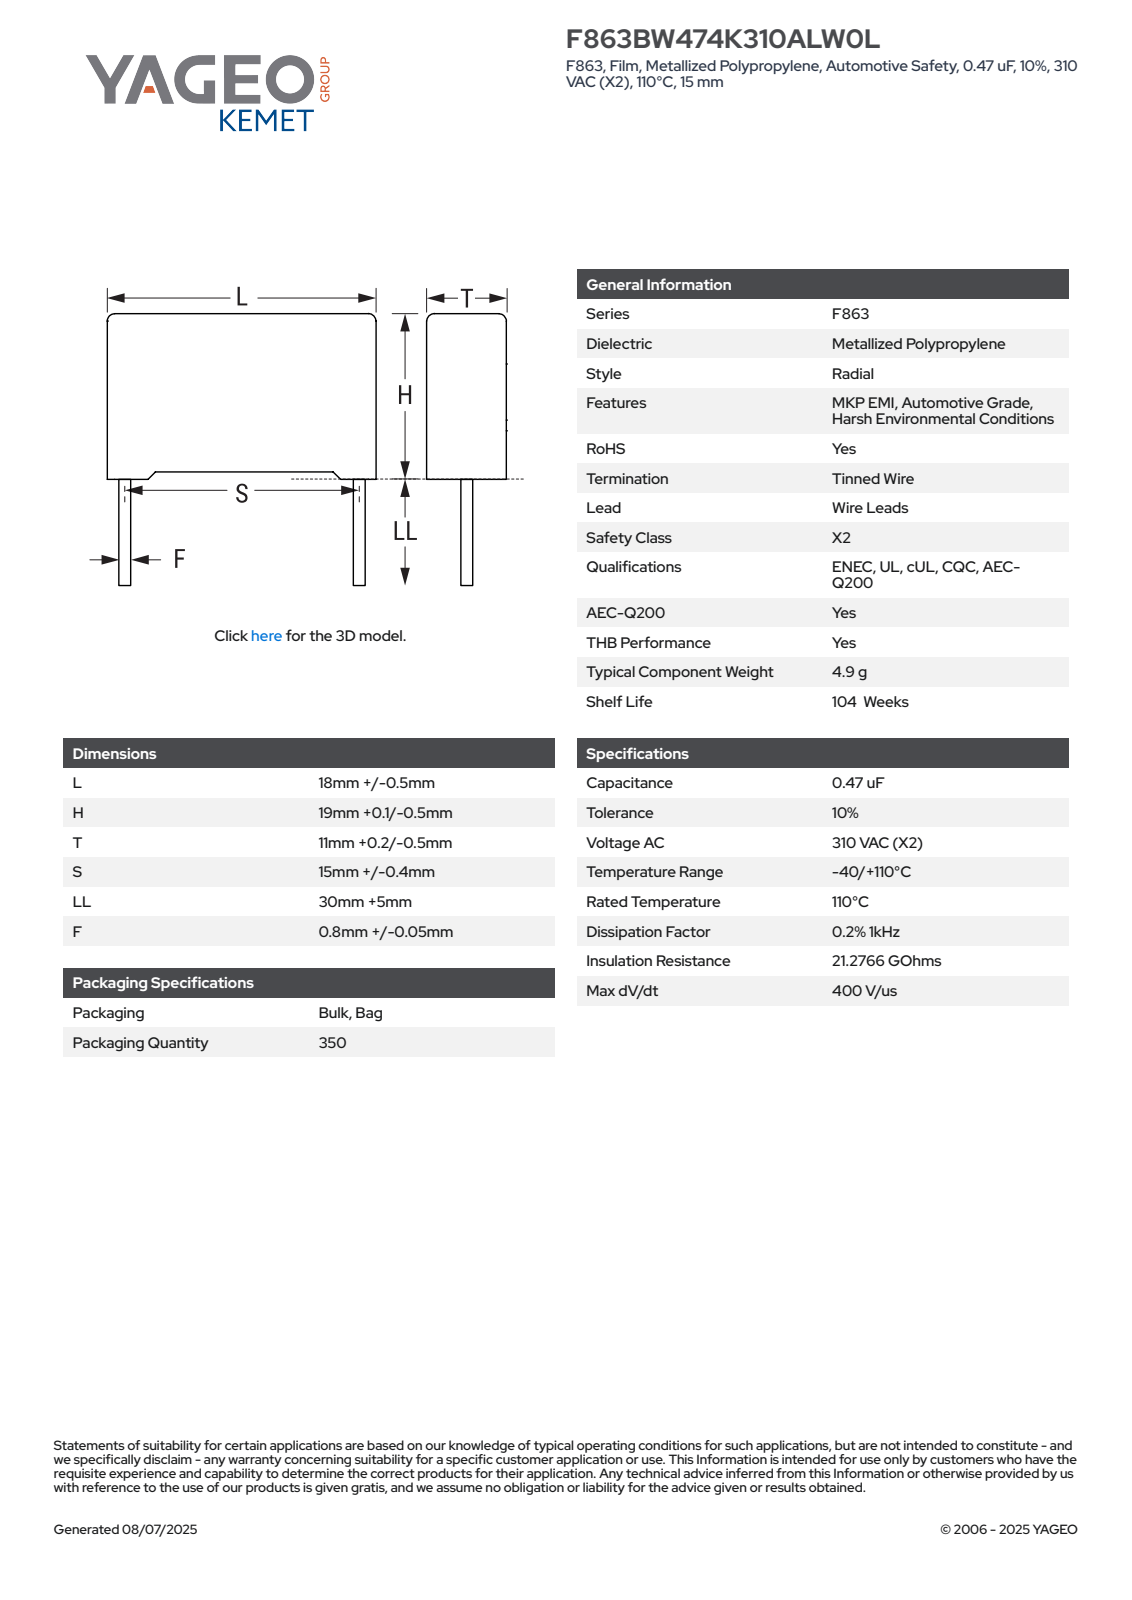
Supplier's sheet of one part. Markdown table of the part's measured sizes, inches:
| quantity | value |
| --- | --- |
| part name | CFR_RB_18X19X11_L18.3H19.1T11.2S15LL35F0.85 |
| STEP written by | SolidWorks 2014 (AUTOMOTIVE_DESIGN) |
| units | inches |
| bodies | 4 solids, 89 faces (81 planar, 8 cylindrical, 0 other) |
| overall size | 2.13 × 0.72 × 0.441 |
| volume | 0.231 in³ |
| surface area | 2.641 in² |
| round bosses / shafts (diameter × count) | 0.033 × 2 |
| partial cylindrical surfaces (radius × count) | 0.027 × 4 |
| main face-to-face distances | 0.441, 0.72, 0.718, 0.441, 0.024, 0.417, 0.034, 0.752, 0.024, 0.394 |
